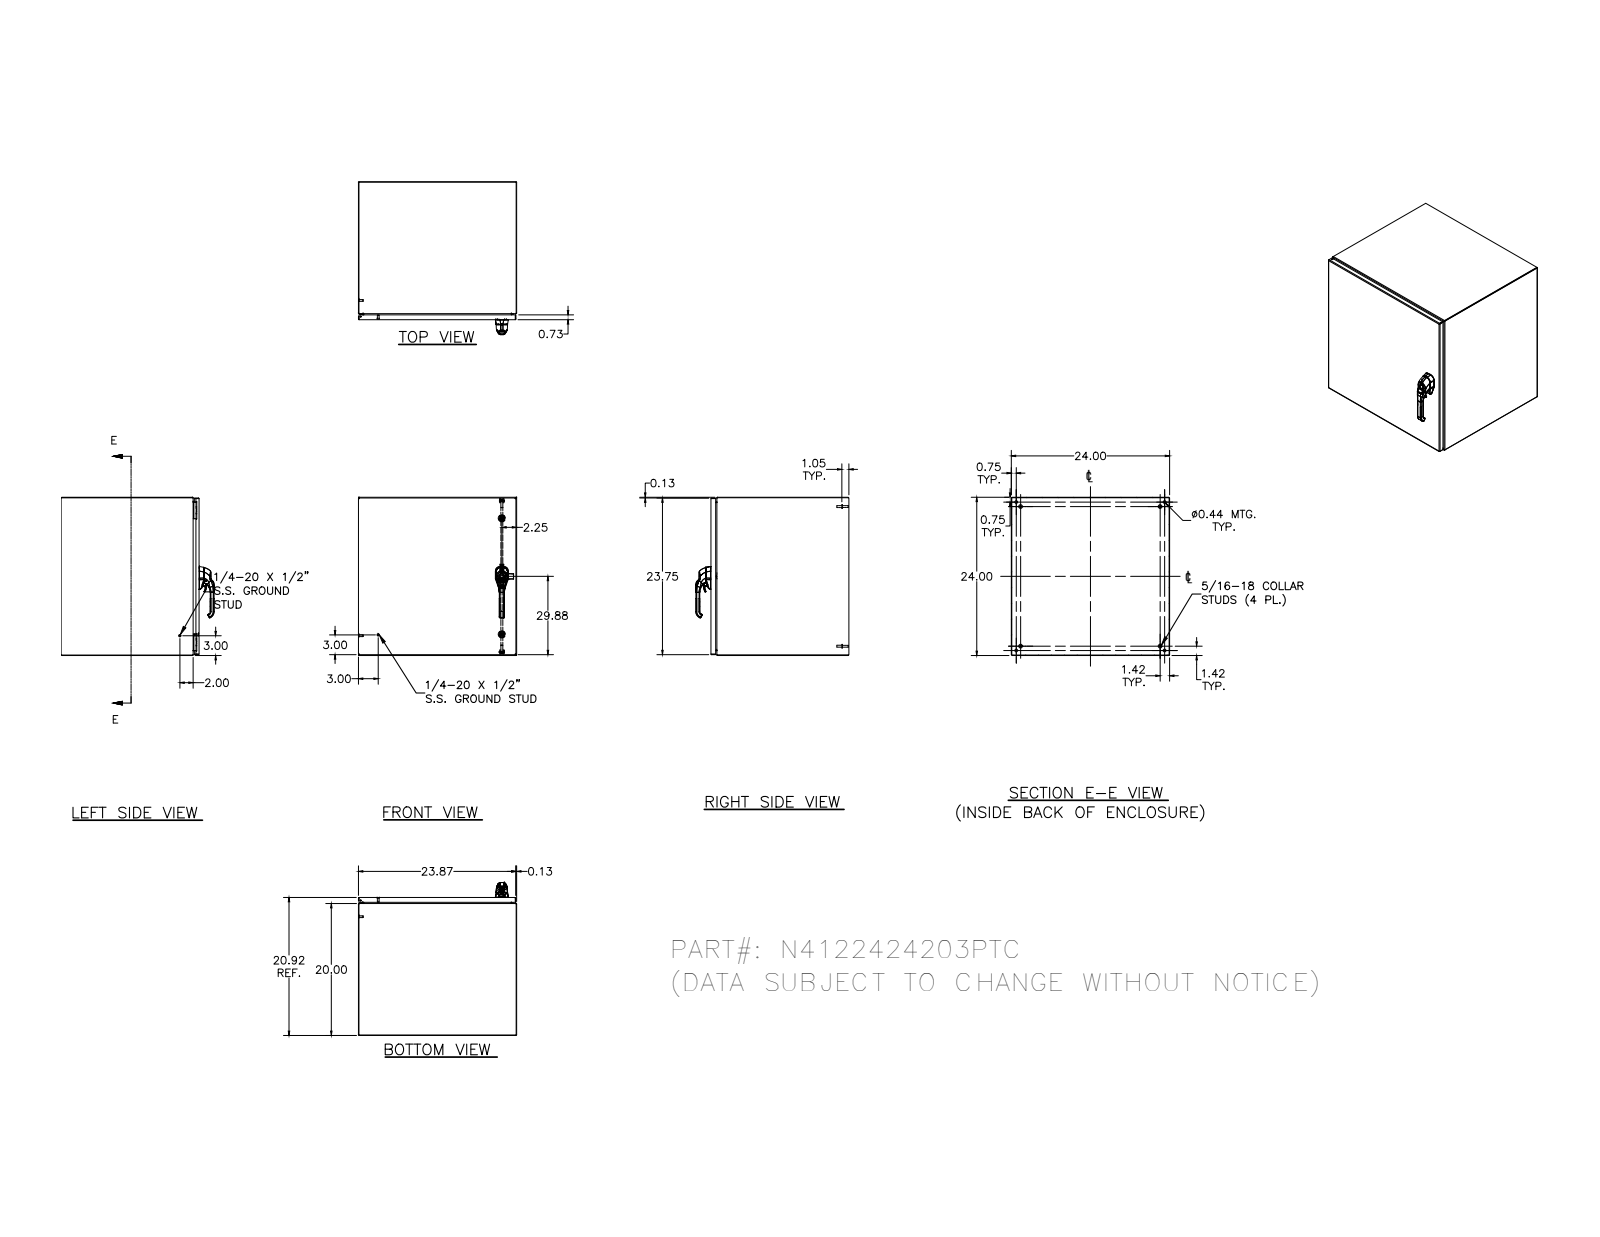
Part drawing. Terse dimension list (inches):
name: N4122424203PTC
written by: SolidWorks 2018 (AUTOMOTIVE_DESIGN)
unit: in
bodies: 53 solids, 1618 faces (587 planar, 576 cylindrical, 455 other)
size: 24 × 24 × 23.095
volume: 254 in³; area: 6 631 in²
holes: 5× ⌀0.188, 4× ⌀0.093, 4× ⌀0.152, 4× ⌀0.165, 4× ⌀0.167, 4× ⌀0.172, 4× ⌀0.197, 4× ⌀0.438, 2× ⌀0.106, 2× ⌀0.156, 2× ⌀0.16, 2× ⌀0.169
bosses: 10× ⌀0.25, 4× ⌀0.563, 4× ⌀0.36, 4× ⌀0.32, 4× ⌀0.3, 4× ⌀0.256, 4× ⌀0.236, 4× ⌀0.164
rounds: 28× R0.031, 26× R0.05, 18× R0.016, 18× R0.02, 18× R0.105, 16× R0.118, 14× R0.125, 8× R0.032
face distances: 0.074, 23.926, 20.843, 23.852, 24, 20.917, 20.769, 19.926, 0.917, 0.739
hole spacings: 20, 0.017, 0.66, 22.5, 21.368, 22.869, 0.019, 0.5
